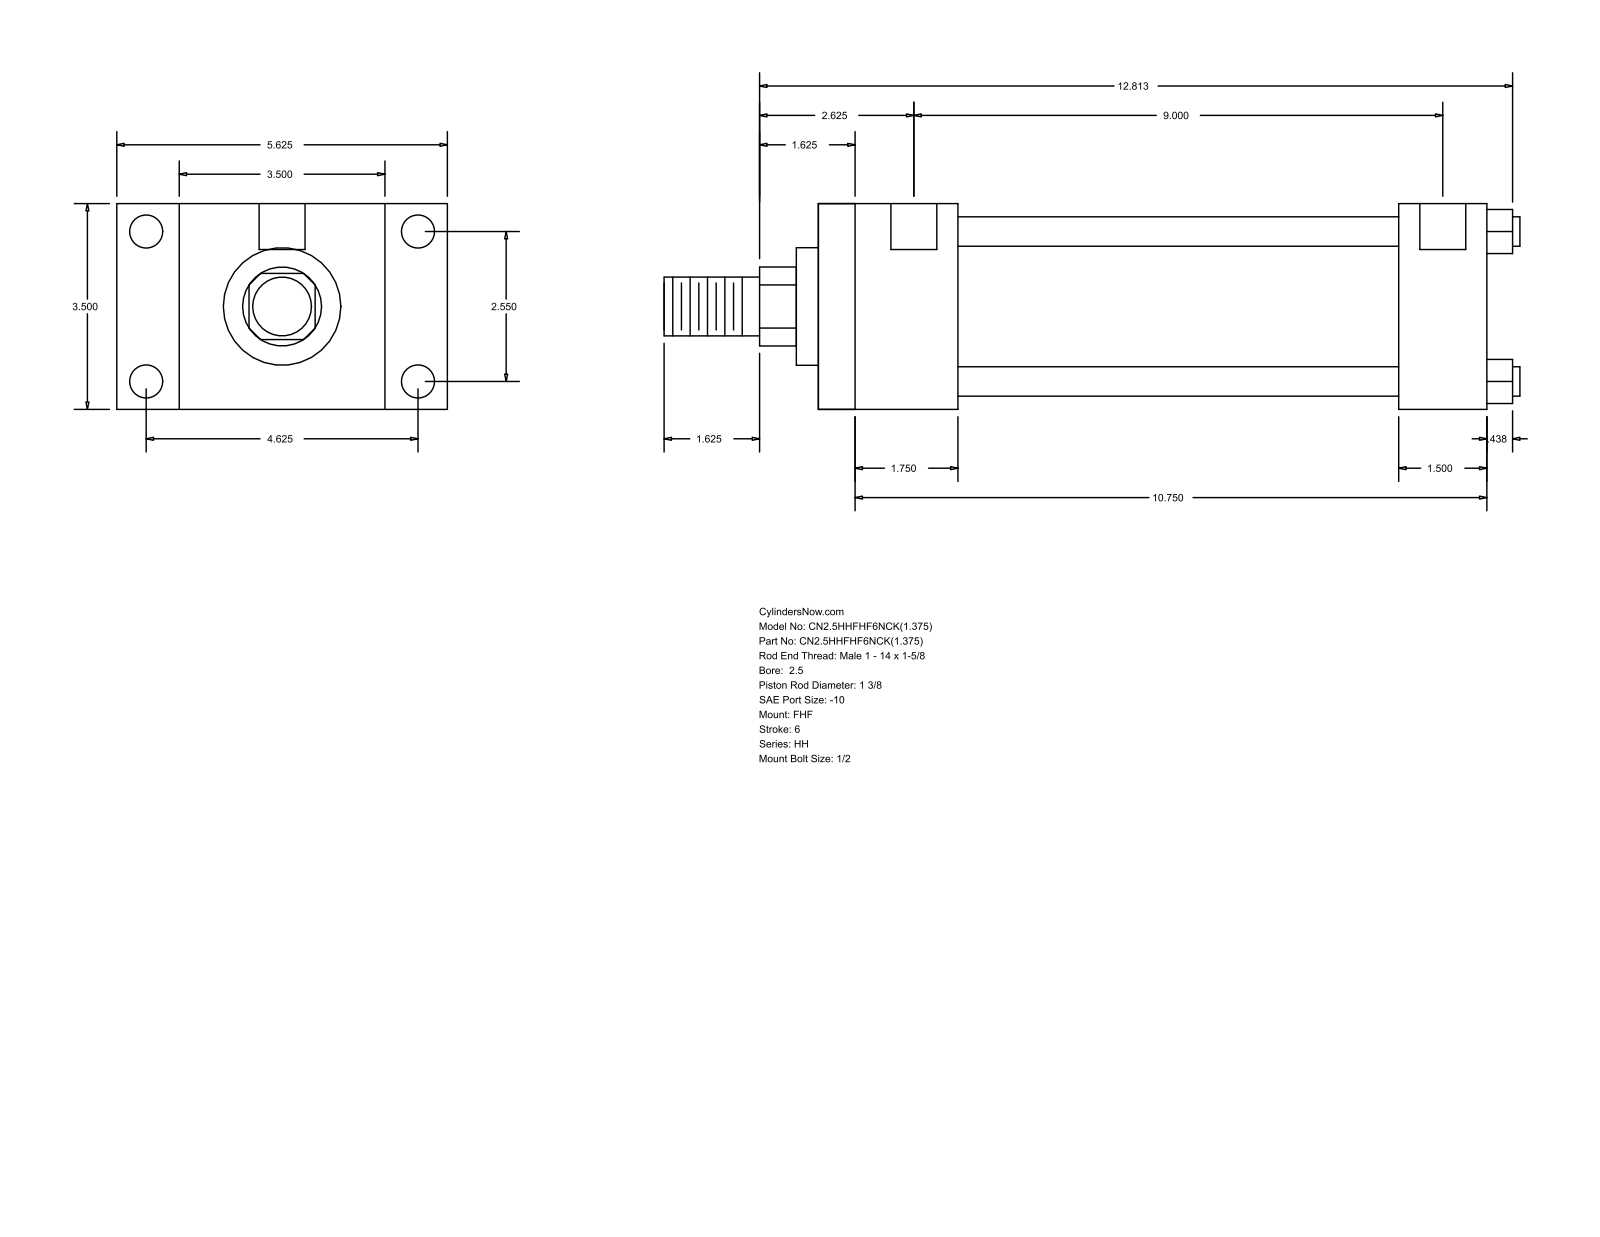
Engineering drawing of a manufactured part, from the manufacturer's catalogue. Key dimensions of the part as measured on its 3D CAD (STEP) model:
Part name (STEP PRODUCT): HH_FHF__0250_1.375
STEP written by: GSSL Pune (CONFIG_CONTROL_DESIGN)
Units: millimetres
Bodies: 0 solids, 88 faces (60 planar, 28 cylindrical, 0 other)
Overall size (bounding box): 369.89 × 142.88 × 88.9
Round holes (diameter × count): ⌀5.56 ×4, ⌀14.3 ×4, ⌀19.84 ×2
Round bosses / shafts (diameter × count): ⌀12.7 ×4, ⌀73.03 ×1, ⌀50.8 ×1, ⌀34.92 ×1, ⌀25.4 ×1
Partial cylindrical surfaces — rounded edges, fillets, slot ends (radius × count): R17.06 ×1
Main face-to-face distances: 88.9, 60.32, 26.99, 115.89, 288.92, 228.6, 142.88, 250.83, 190.51, 38.09
Hole centre spacings: 64.76, 117.48, 134.15, 231.77, 1.58, 1.59, 228.6, 230.18
